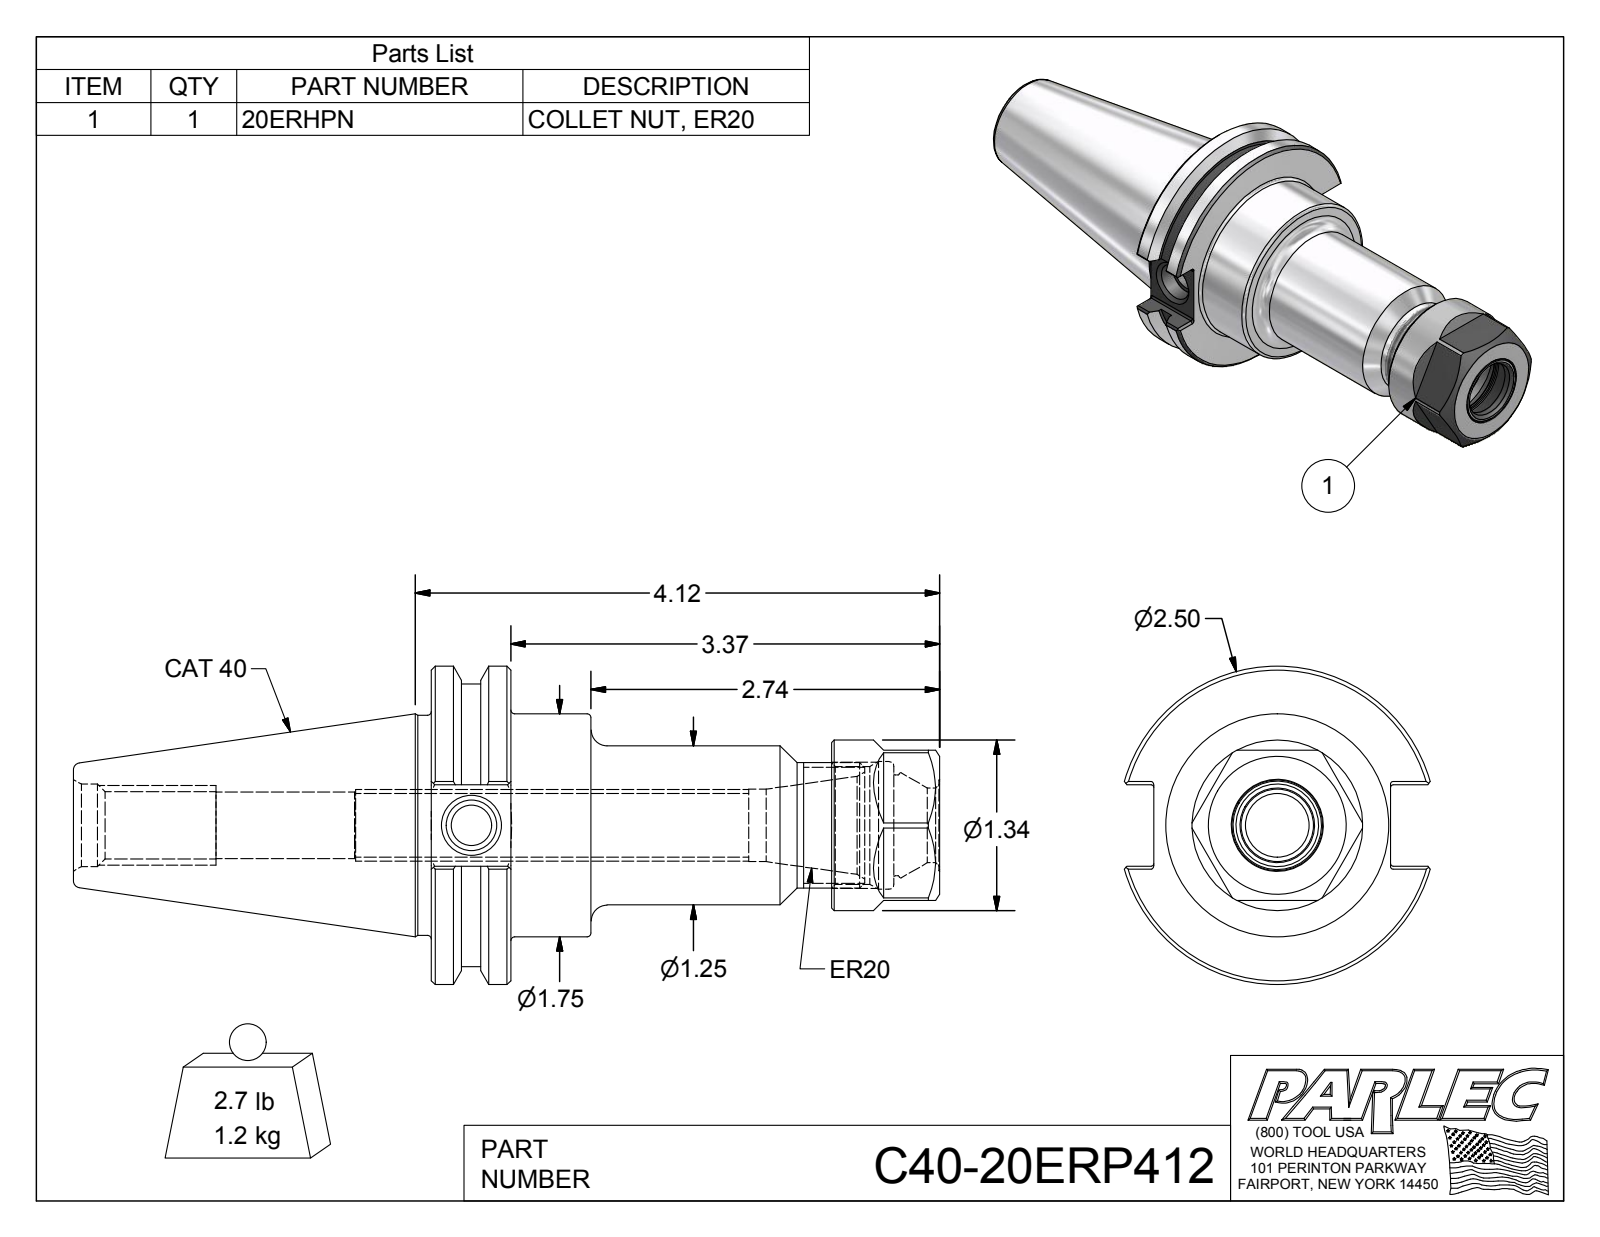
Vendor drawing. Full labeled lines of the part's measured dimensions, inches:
Part name (STEP PRODUCT): C40-20ERP412; C40-20ER4-1; 20ERHPN
STEP written by: Autodesk Inventor 2012 (AUTOMOTIVE_DESIGN)
Units: inches
Bodies: 2 solids, 120 faces (49 planar, 34 cylindrical, 37 other)
Overall size (bounding box): 6.808 × 2.5 × 2.403
Volume: 9.952 in³ · Surface area: 54.11 in²
Round holes (diameter × count): ⌀0.315 ×1, ⌀0.399 ×1, ⌀0.502 ×1, ⌀0.525 ×1, ⌀0.527 ×1, ⌀0.57 ×1, ⌀0.587 ×1, ⌀0.648 ×1, ⌀0.79 ×1, ⌀0.926 ×1, ⌀1.005 ×1
Round bosses / shafts (diameter × count): ⌀2.5 ×1, ⌀2.219 ×1, ⌀1.75 ×1, ⌀1.73 ×1, ⌀1.34 ×1, ⌀1.25 ×1, ⌀0.984 ×1
Partial cylindrical surfaces — rounded edges, fillets, slot ends (radius × count): R0.02 ×12
Main face-to-face distances: 0.625, 1.18, 3.145, 2.52, 3.995, 3.37, 0.85, 1.255, 0.63, 1.89
